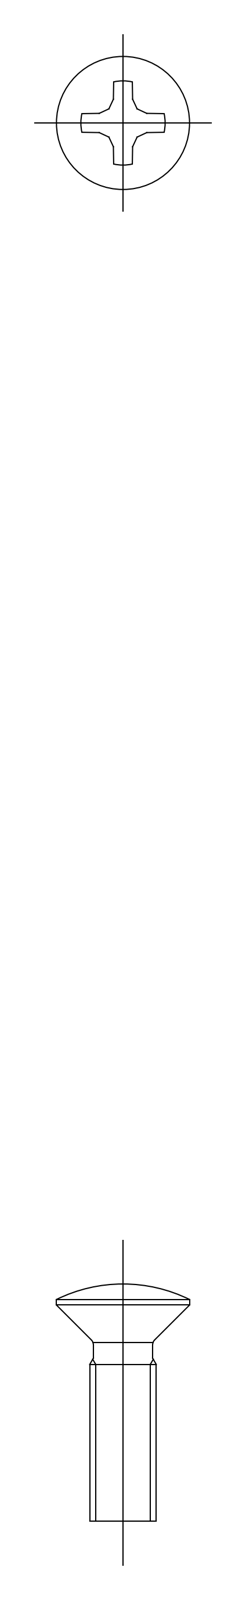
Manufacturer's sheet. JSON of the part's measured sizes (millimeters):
{"part_name": "screw", "step_written_by": "CADfix (AUTOMOTIVE_DESIGN)", "units": "millimeters", "bodies": {"solids": 1, "faces": 27, "planar": 0, "cylindrical": 0, "other": 27}, "overall_size": [10.67, 6, 6], "volume_mm3": 96, "surface_area_mm2": 157}
